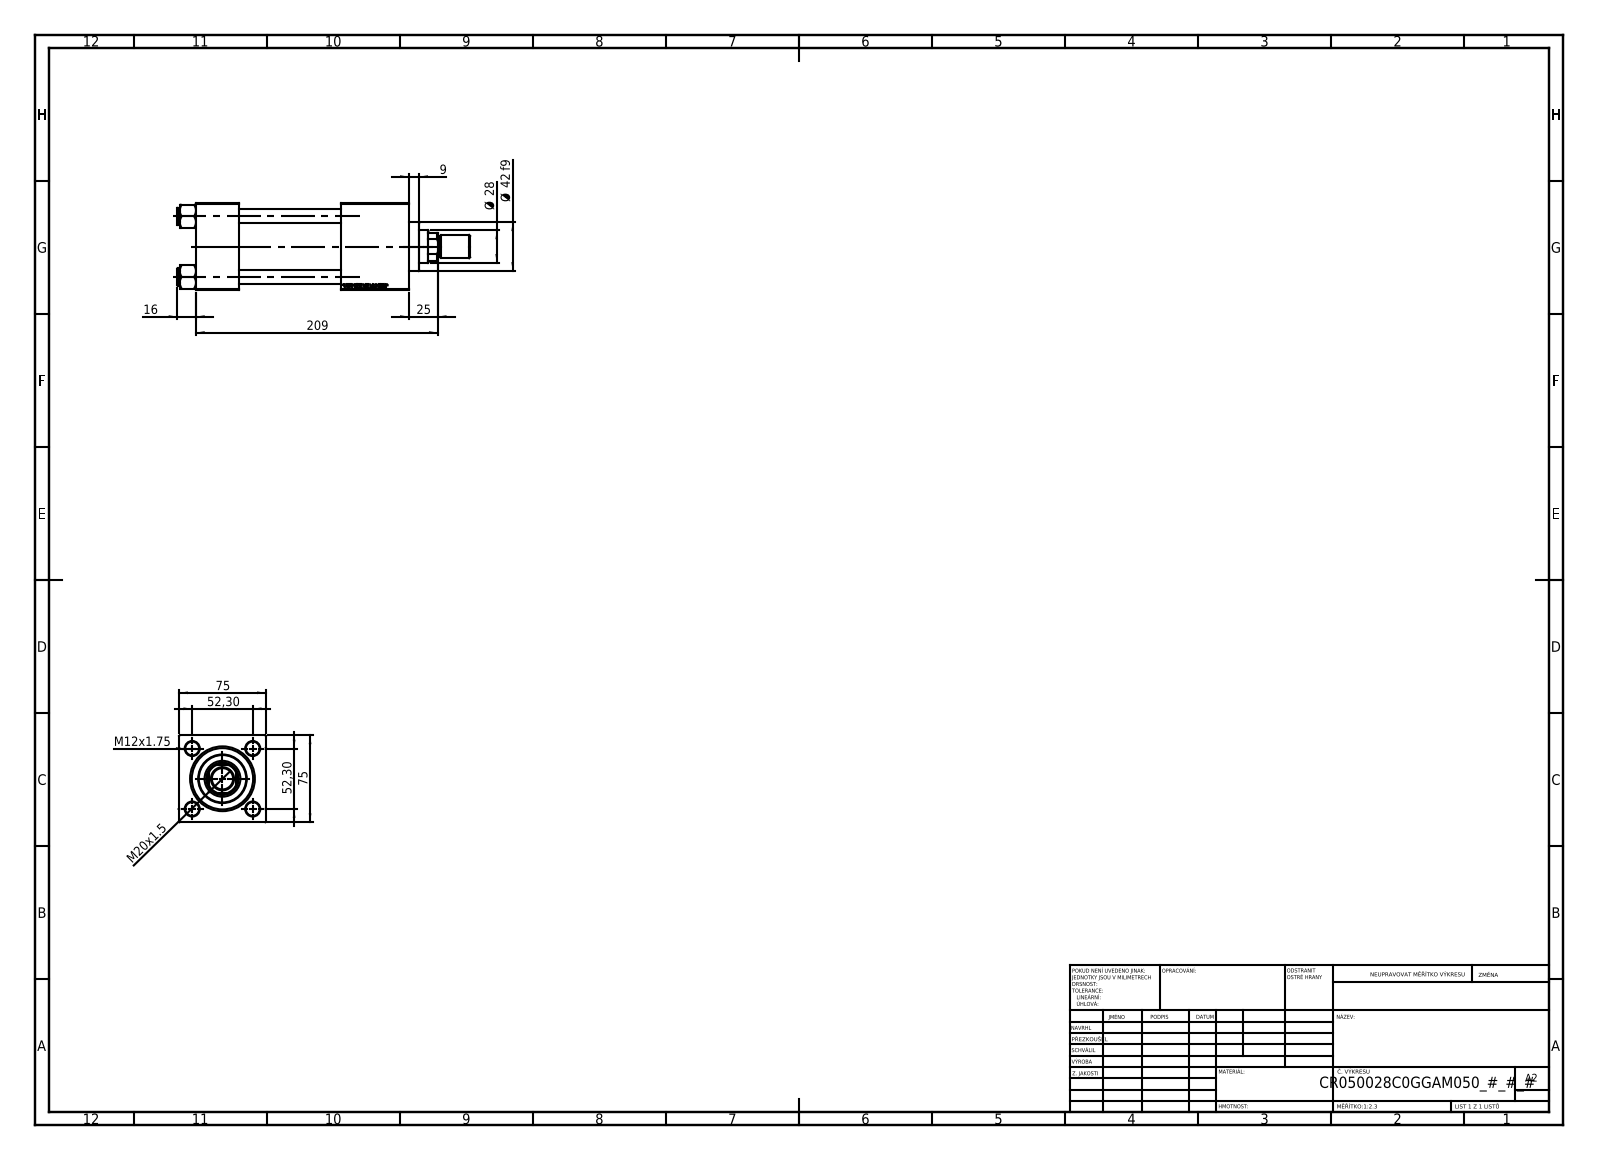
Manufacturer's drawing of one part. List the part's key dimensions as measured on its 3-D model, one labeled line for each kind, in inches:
Part name (STEP PRODUCT): NUT_M5_C; V215CR_C_Body; ROD_END_AH; V215CR_VCP_C (+2 more)
STEP written by: SolidWorks 2019 (CONFIG_CONTROL_DESIGN)
Units: inches
Bodies: 12 solids, 1163 faces (530 planar, 91 cylindrical, 542 other)
Overall size (bounding box): 9.961 × 2.974 × 2.953
Volume: 44.22 in³ · Surface area: 264.3 in²
Round holes (diameter × count): ⌀0.472 ×4, ⌀0.276 ×2, ⌀0.825 ×2, ⌀1.181 ×2, ⌀0.728 ×1, ⌀1.102 ×1, ⌀1.22 ×1, ⌀1.614 ×1, ⌀1.969 ×1, ⌀2.087 ×1
Round bosses / shafts (diameter × count): ⌀0.591 ×4, ⌀2.205 ×1, ⌀1.654 ×1, ⌀0.787 ×1, ⌀0.709 ×1
Partial cylindrical surfaces — rounded edges, fillets, slot ends (radius × count): R0.531 ×1
Main face-to-face distances: 2.953, 1.457, 7.244, 5.787, 2.323, 4.921, 3.465, 6.114, 4.657, 1.193
Hole centre spacings: 1.456, 2.059, 2.912, 4.862
